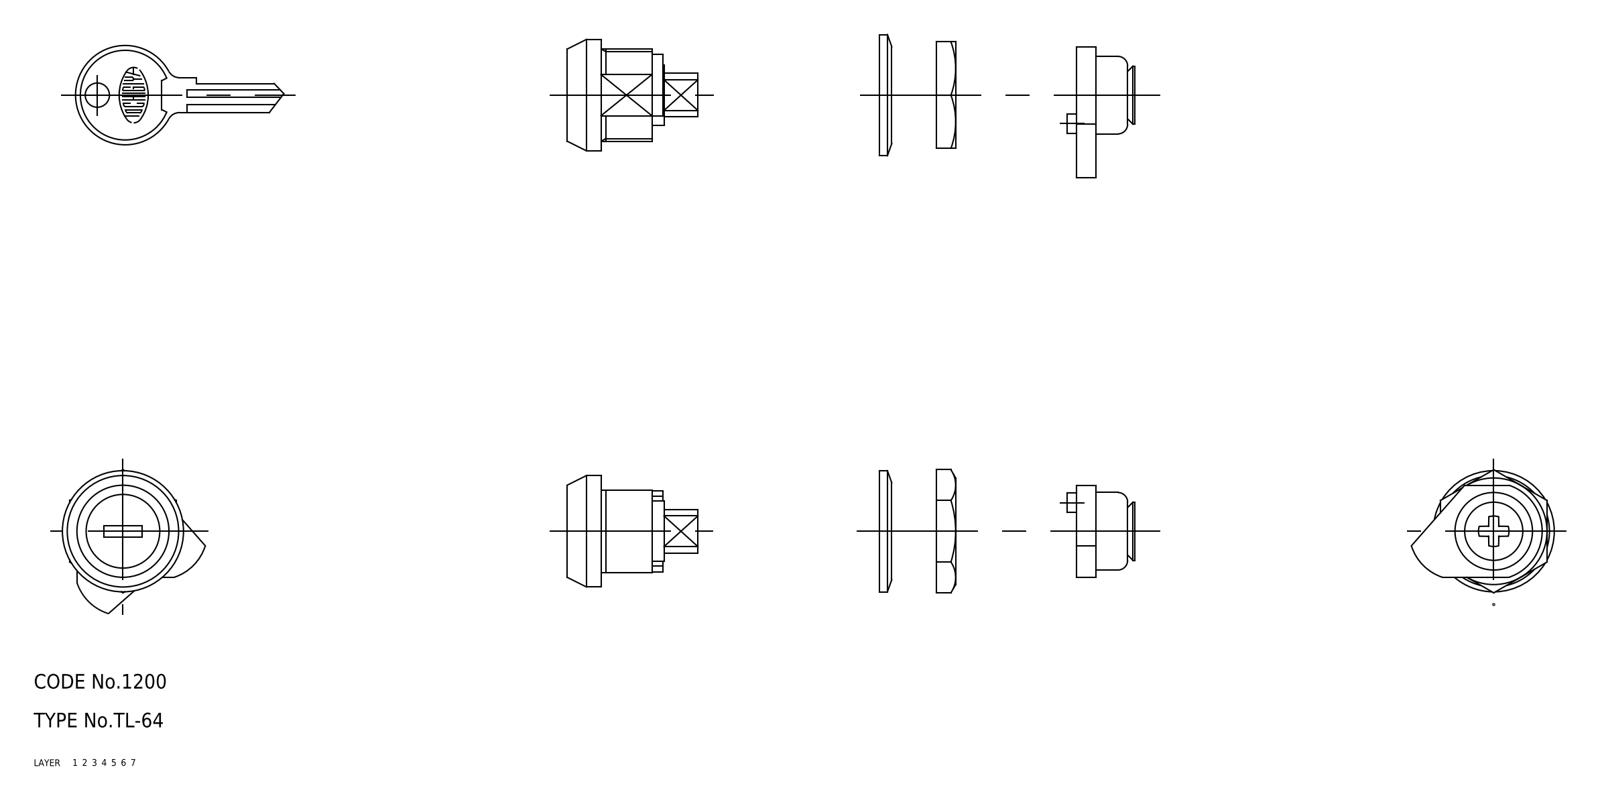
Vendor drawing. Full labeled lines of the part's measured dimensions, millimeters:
Part name (STEP PRODUCT): washer_2; washer_1; screw; nut (+4 more)
STEP written by: CADfix (AUTOMOTIVE_DESIGN)
Units: millimetres
Bodies: 8 solids, 134 faces (0 planar, 0 cylindrical, 134 other)
Overall size (bounding box): 93.49 × 29.5 × 25.4
Volume: 9 875 mm³ · Surface area: 9 247 mm²
